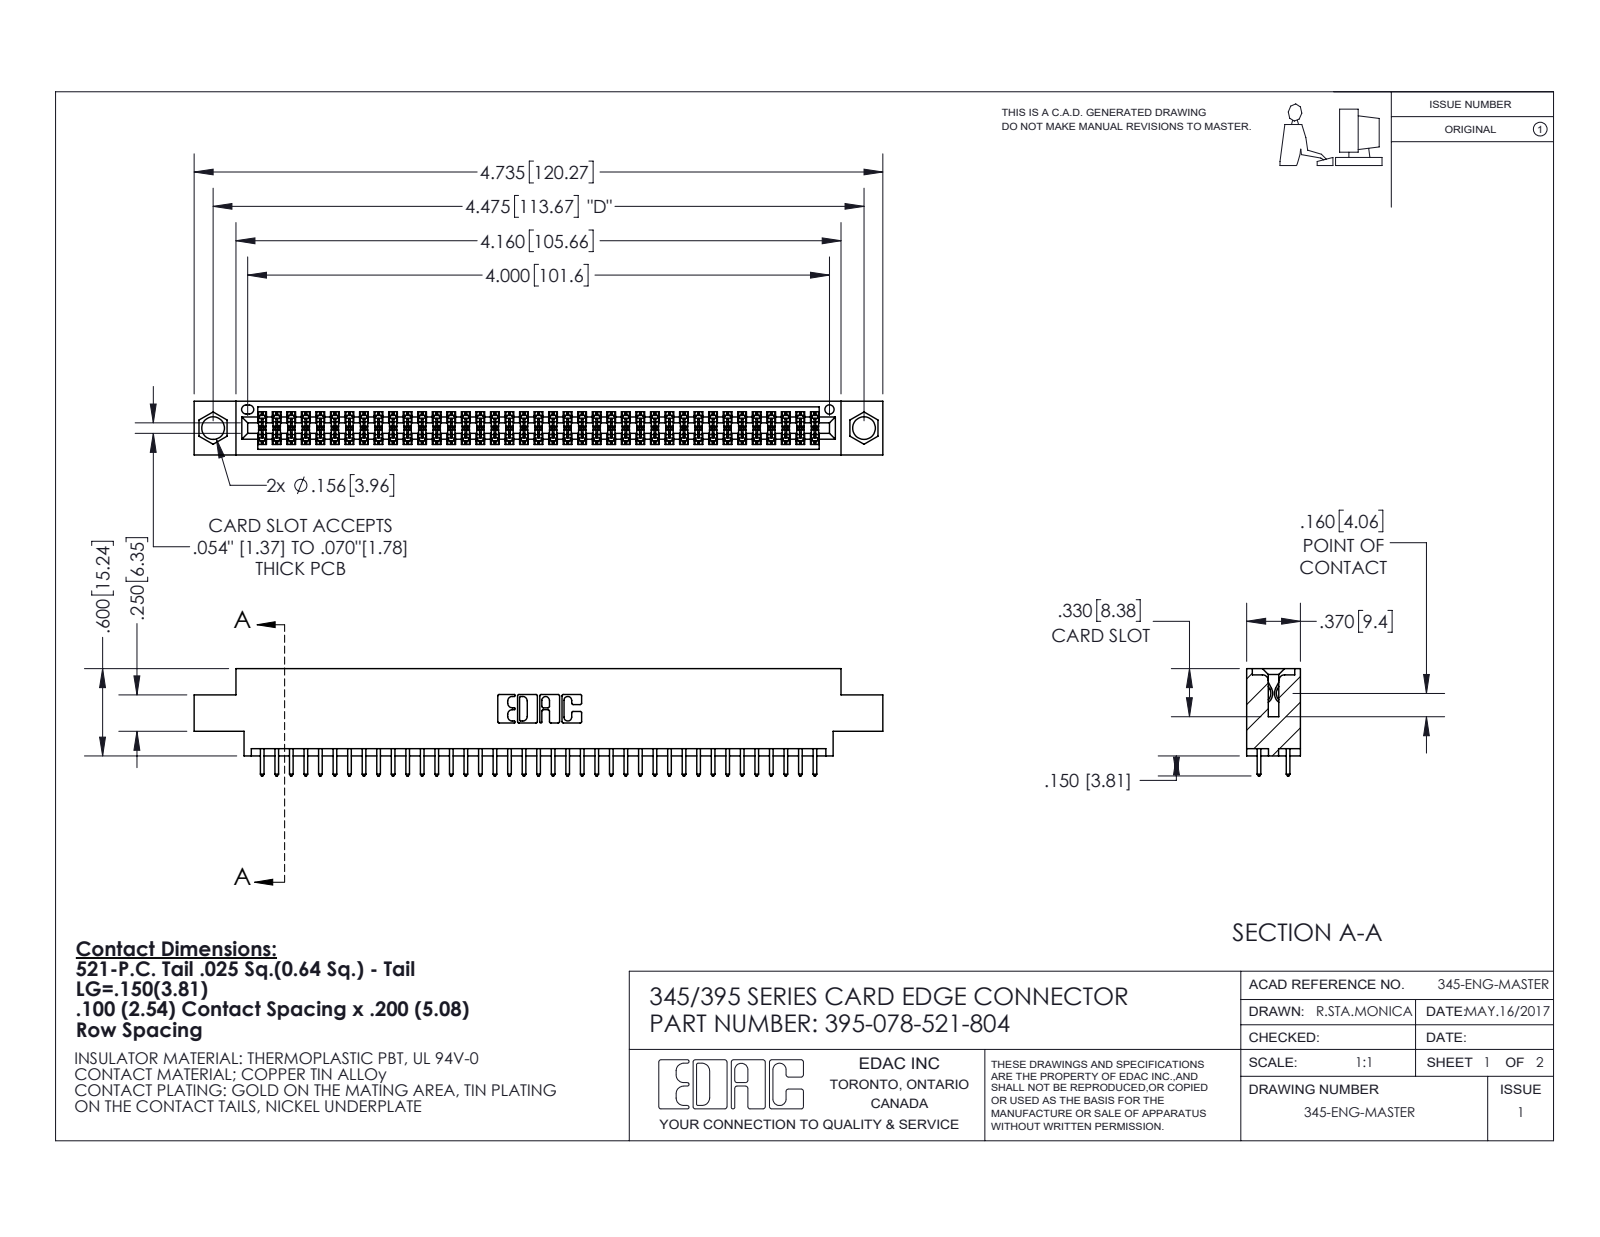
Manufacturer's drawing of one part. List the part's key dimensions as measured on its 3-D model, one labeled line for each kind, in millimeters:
Part name (STEP PRODUCT): 345 Part_0.170 Offset - 0.156 Dia-TI; 345-292-001_345-293-121; 395-078-521-804
STEP written by: SolidWorks 2020 (CONFIG_CONTROL_DESIGN)
Units: millimetres
Bodies: 79 solids, 4044 faces (2672 planar, 1372 cylindrical, 0 other)
Overall size (bounding box): 120.3 × 18.7 × 9.4
Volume: 11 400 mm³ · Surface area: 16 590 mm²
Round holes (diameter × count): ⌀4 ×2, ⌀1.6 ×1
Partial cylindrical surfaces — rounded edges, fillets, slot ends (radius × count): R0.2 ×156, R0.3 ×78, R0.3 ×22, R0.2 ×6, R0.8 ×6, R0.7 ×3, R0.4 ×2, R0.5 ×2
Main face-to-face distances: 1.8, 7.6, 9.4, 5.1, 2.5, 6.9, 0.6, 5.7, 4.4, 3.8
Hole centre spacings: 6.9, 107.7, 113.7
